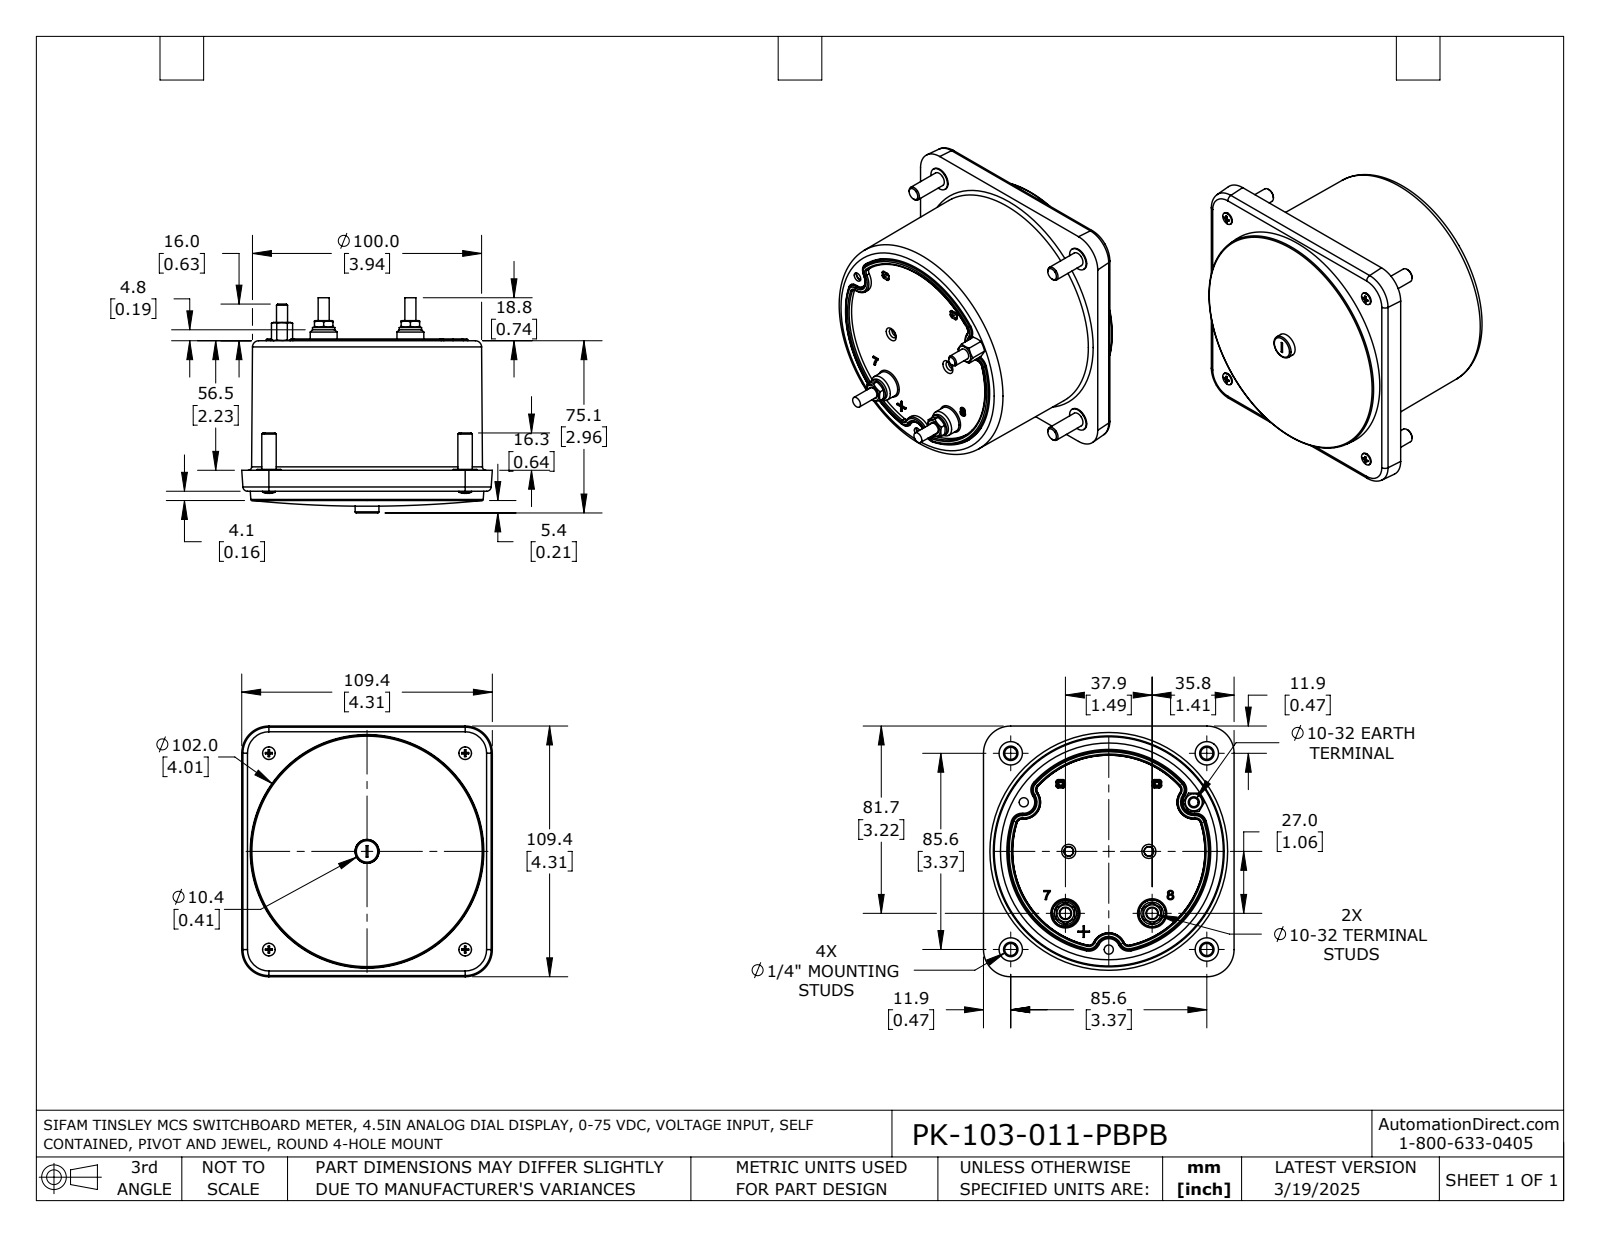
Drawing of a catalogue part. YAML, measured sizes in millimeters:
part_name: "PK-103-011-PBPB"
step_written_by: "SolidWorks 2021 (AUTOMOTIVE_DESIGN)"
units: millimeters
bodies: {solids: 1, faces: 609, planar: 167, cylindrical: 141, other: 301}
overall_size: [109.4, 109.4, 93.9]
volume: 594500
surface_area: 53040
round_holes:
  - {diameter: 2.4, count: 4}
  - {diameter: 3.5, count: 4}
  - {diameter: 8, count: 4}
  - {diameter: 4, count: 3}
  - {diameter: 5.3, count: 2}
round_bosses_or_shafts:
  - {diameter: 10.2, count: 4}
  - {diameter: 6.3, count: 4}
  - {diameter: 5.5, count: 4}
  - {diameter: 2.9, count: 4}
  - {diameter: 4.8, count: 3}
  - {diameter: 9.8, count: 2}
  - {diameter: 3.7, count: 1}
partial_cylinders:
  - {radius: 0.5, count: 24}
  - {radius: 4.8, count: 9}
  - {radius: 2, count: 4}
  - {radius: 44.5, count: 1}
face_to_face_distances: [55.3, 64.4, 9.1, 1.2, 56.5, 65.7, 12.4, 69, 67.7, 3.3]
hole_center_spacings: [85.6, 85.6, 85.7, 85.8, 85.9, 121.1, 24.7, 28.6]
